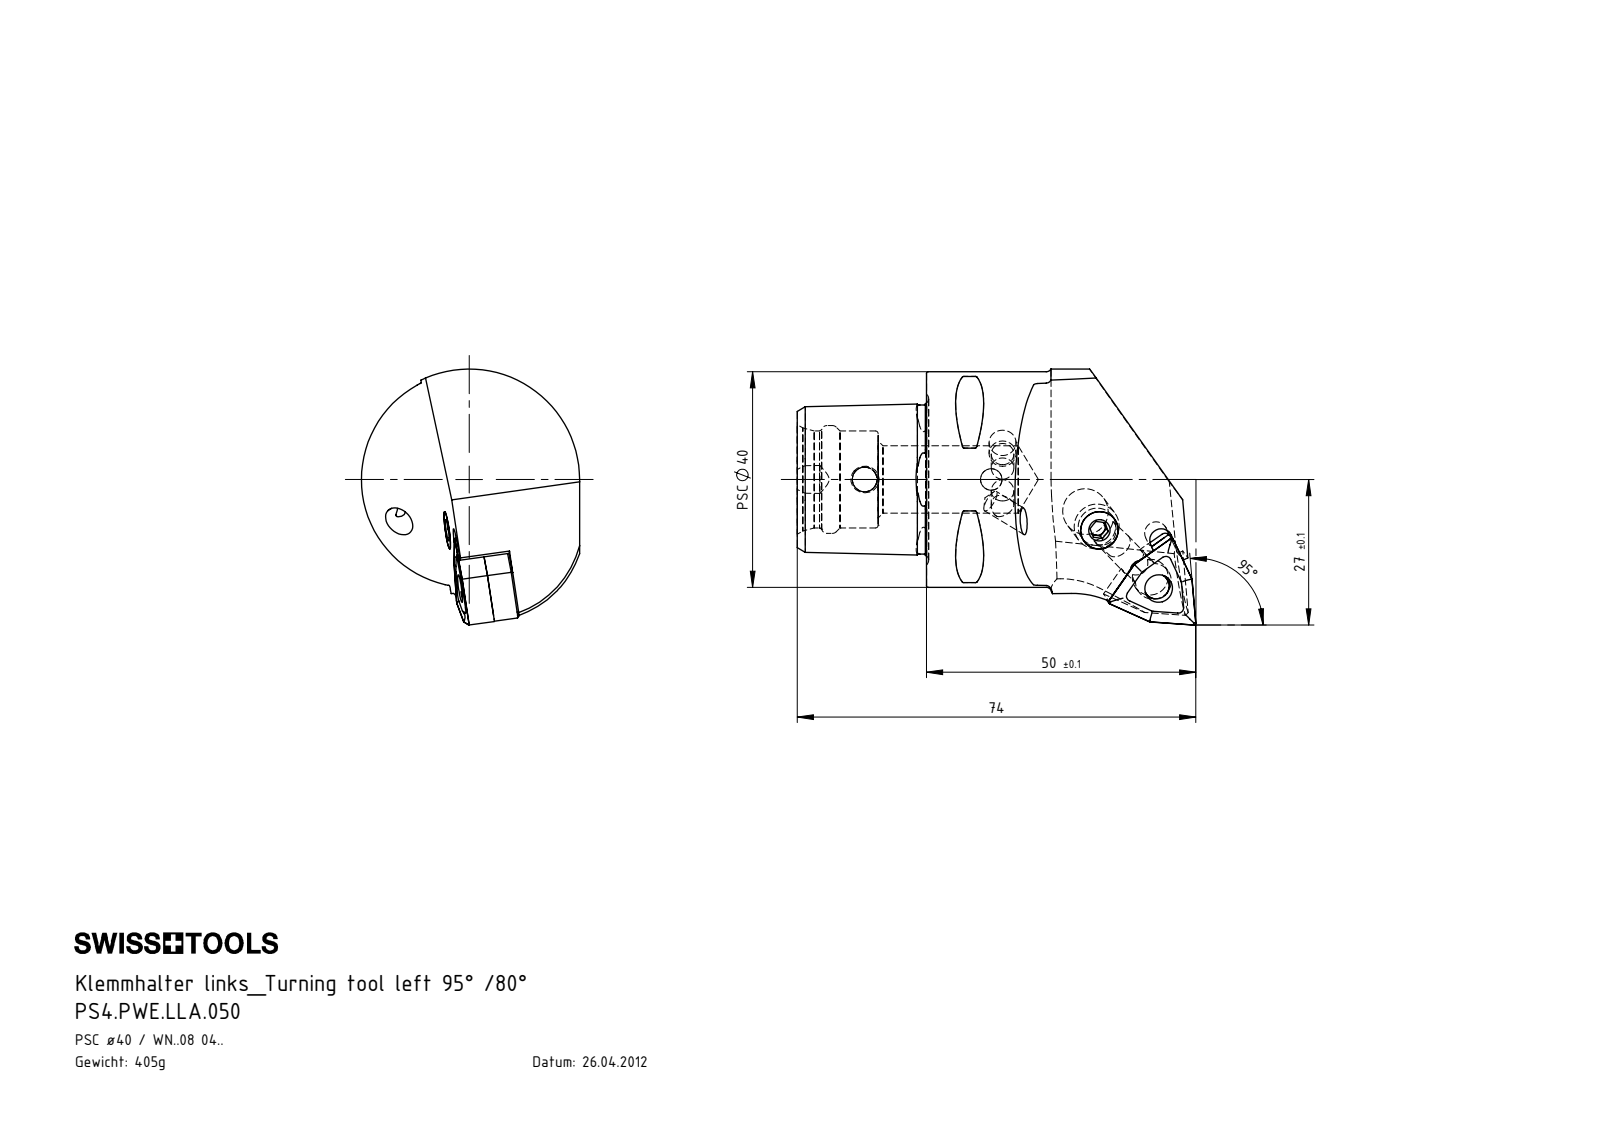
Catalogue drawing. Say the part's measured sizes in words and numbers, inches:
The part is named "PS4-PWE.LLA.050; KVT_MB_600_050; WCD-ER1.101.000; WCD-ER4.101.017_A (+4 more)". Its 3-D file was written by "SolidWorks 2012 (CONFIG_CONTROL_DESIGN)". It is 8 solids with 367 faces: 101 planar, 86 cylindrical and 180 other. Overall it measures 2.913 by 1.87 by 1.594 inches. Its volume is 3.115 cubic inches and its surface area 24.38 square inches. Round holes: 2 of diameter 0.157, 2 of diameter 0.165, 2 of diameter 0.264, 1 of diameter 0.181, 1 of diameter 0.197, 1 of diameter 0.203, 1 of diameter 0.276, 1 of diameter 0.307, 1 of diameter 0.331, 1 of diameter 0.492, 1 of diameter 0.709, 1 of diameter 0.787. Round bosses or shafts: 1 of diameter 1.575, 1 of diameter 0.315, 1 of diameter 0.311, 1 of diameter 0.252, 1 of diameter 0.197, 1 of diameter 0.185, 1 of diameter 0.14. Partial cylindrical surfaces (rounded edges, fillets, slot ends): 8 of radius 0.012, 3 of radius 0.016, 3 of radius 0.039, 2 of radius 0.098, 1 of radius 0.031, 1 of radius 0.079, 1 of radius 0.083, 1 of radius 0.093. The main face-to-face distances are 0.175, 0.187, 0.945, 0.363, 0.363, 0.611, 0.188, 0.22, 0.221, 0.408. The hole center spacings are 0.614, 0.925.
